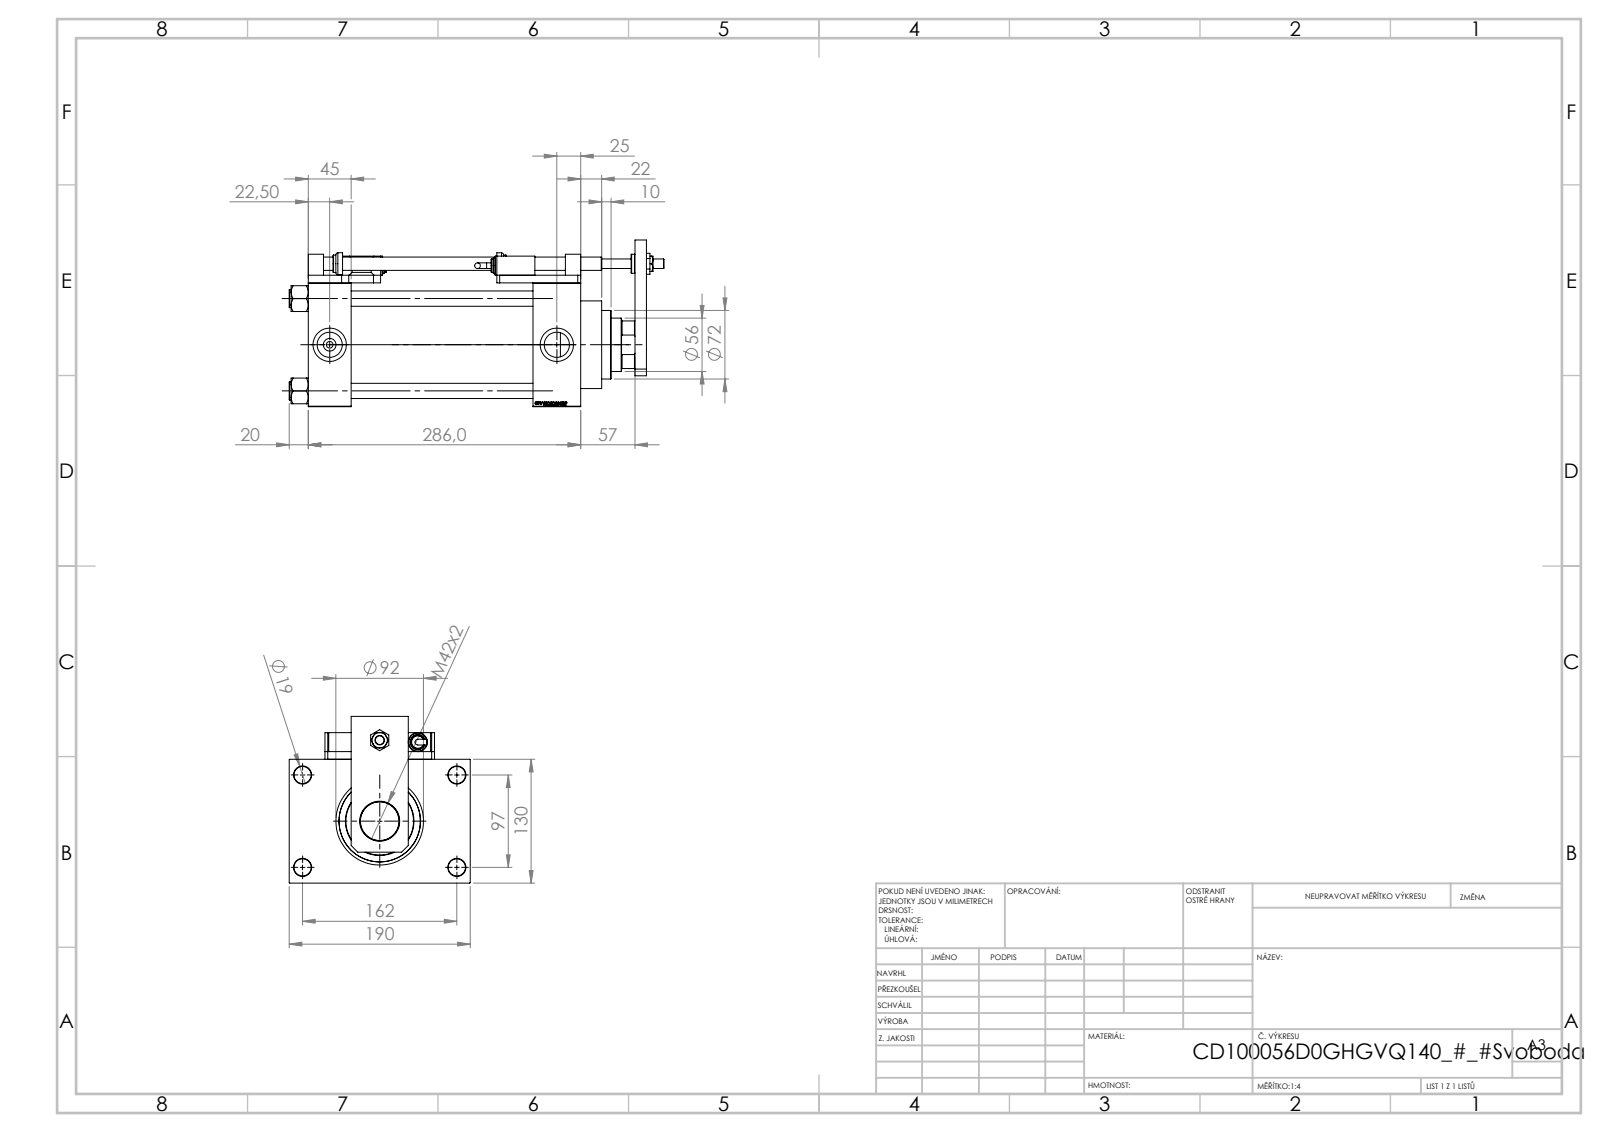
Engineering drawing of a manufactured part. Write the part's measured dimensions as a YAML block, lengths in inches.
part_name: "V215CD_VC_A; V215CD_VCP_D; V215CD_SWITCH_Q_DIMA; V215CD_SWITCH_Q_NUT (+7 more)"
step_written_by: "SolidWorks 2019 (CONFIG_CONTROL_DESIGN)"
units: inches
bodies: {solids: 24, faces: 1379, planar: 666, cylindrical: 156, other: 557}
overall_size: [15.492, 7.48, 6.89]
volume: 212.2
surface_area: 909.9
round_holes:
  - {diameter: 0.335, count: 4}
  - {diameter: 0.531, count: 4}
  - {diameter: 0.63, count: 4}
  - {diameter: 0.709, count: 4}
  - {diameter: 0.276, count: 2}
  - {diameter: 1.041, count: 2}
  - {diameter: 1.378, count: 2}
  - {diameter: 0.394, count: 1}
  - {diameter: 0.551, count: 1}
  - {diameter: 1.594, count: 1}
  - {diameter: 1.654, count: 1}
  - {diameter: 2.205, count: 1}
round_bosses_or_shafts:
  - {diameter: 0.748, count: 4}
  - {diameter: 0.787, count: 3}
  - {diameter: 0.63, count: 2}
  - {diameter: 0.551, count: 2}
  - {diameter: 0.236, count: 2}
  - {diameter: 4.173, count: 1}
  - {diameter: 3.622, count: 1}
  - {diameter: 2.835, count: 1}
partial_cylinders:
  - {radius: 0.295, count: 4}
  - {radius: 1.063, count: 1}
face_to_face_distances: [1.772, 5.118, 11.26, 9.488, 0.315, 1.969, 9.291, 7.52, 5.433, 1.181]
hole_center_spacings: [1.281, 2.698, 3.717, 3.815, 4.026, 5.096, 6.367, 1.26]
